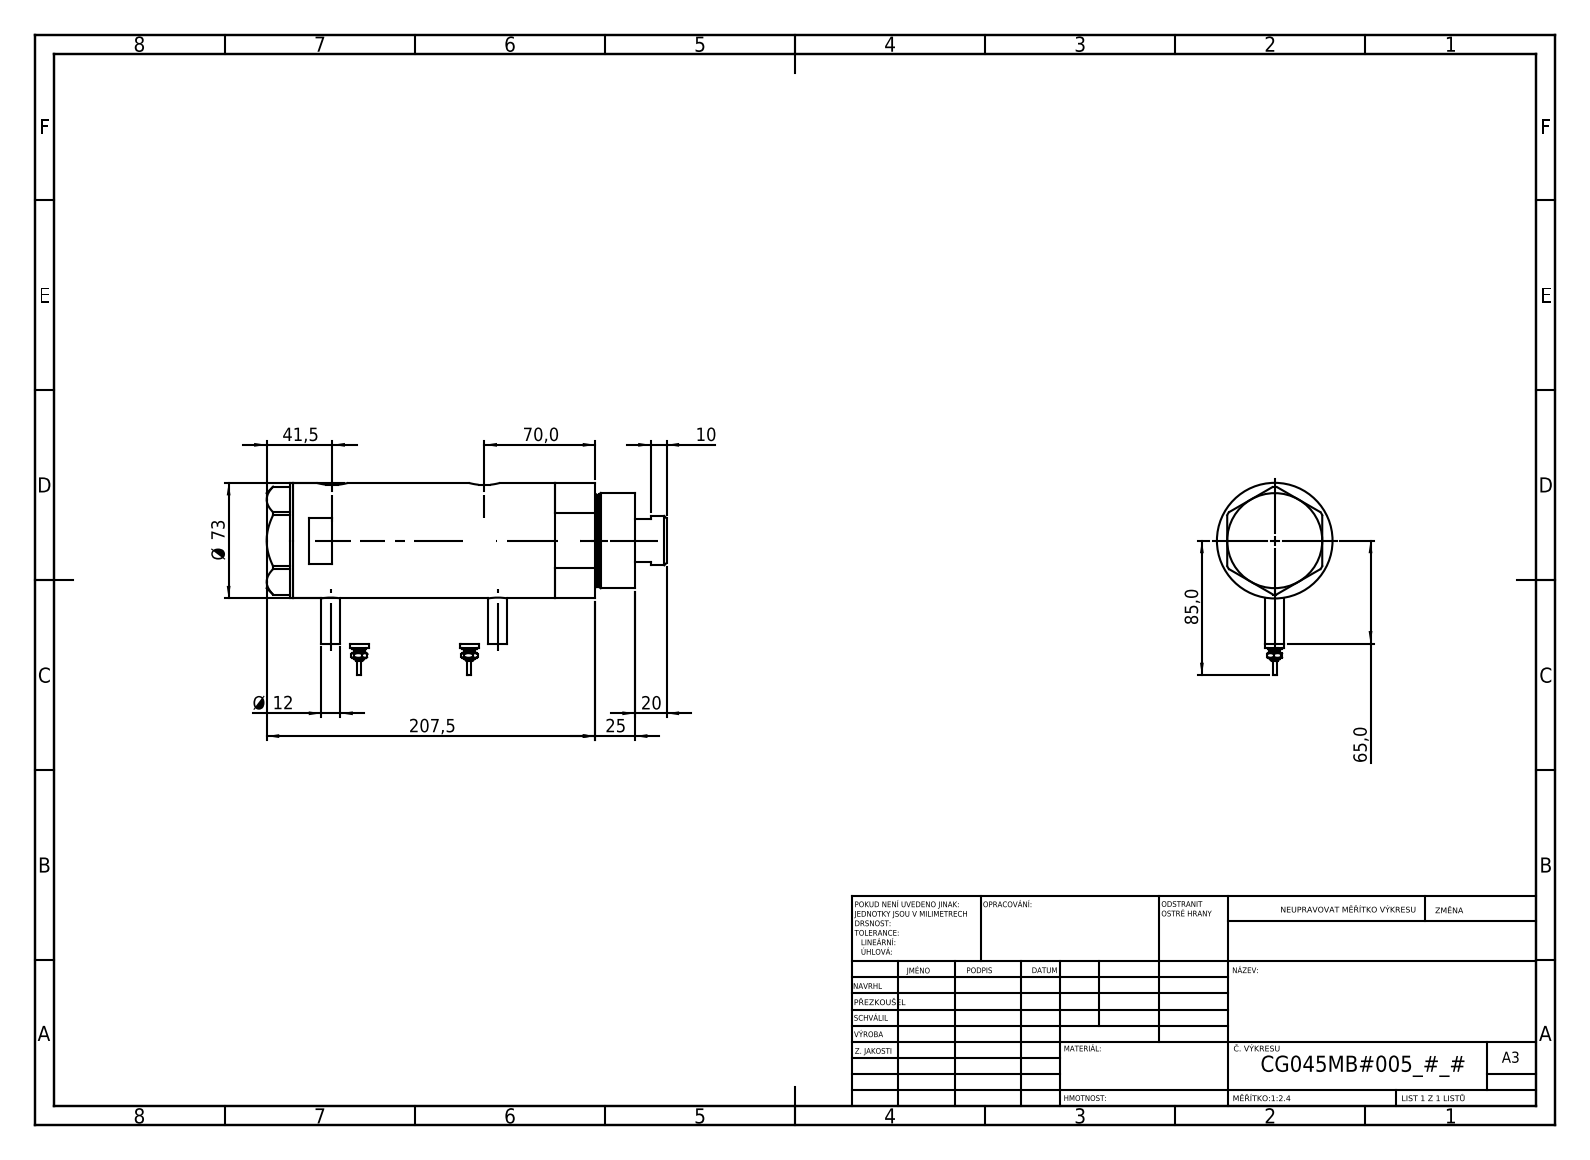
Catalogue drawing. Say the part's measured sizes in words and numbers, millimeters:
The part is named "V270CG_MIDDLE; V270CG_BACK; V270CG_FRONT; Switch (+1 more)". Its 3-D file was written by "SolidWorks 2019 (CONFIG_CONTROL_DESIGN)". It is 6 solids with 212 faces: 77 planar, 71 cylindrical and 64 other. Overall it measures 252.5 by 121.5 by 73 millimeters. Its volume is 927 537 cubic millimeters and its surface area 153 567 square millimeters. Round holes: 2 of diameter 12.5, 2 of diameter 13.16, 1 of diameter 10.5, 1 of diameter 32, 1 of diameter 33.5, 1 of diameter 45, 1 of diameter 48, 1 of diameter 64. Round bosses or shafts: 4 of diameter 12, 2 of diameter 9, 2 of diameter 7, 2 of diameter 4.5, 2 of diameter 2.5, 1 of diameter 73, 1 of diameter 60, 1 of diameter 58. Partial cylindrical surfaces (rounded edges, fillets, slot ends): 2 of radius 10. The main face-to-face distances are 95, 121, 26, 16.5, 42.5, 137.5, 2, 216, 232.5, 190. The hole center spacings are 1, 8.5, 96, 97, 104.5, 105.5.
